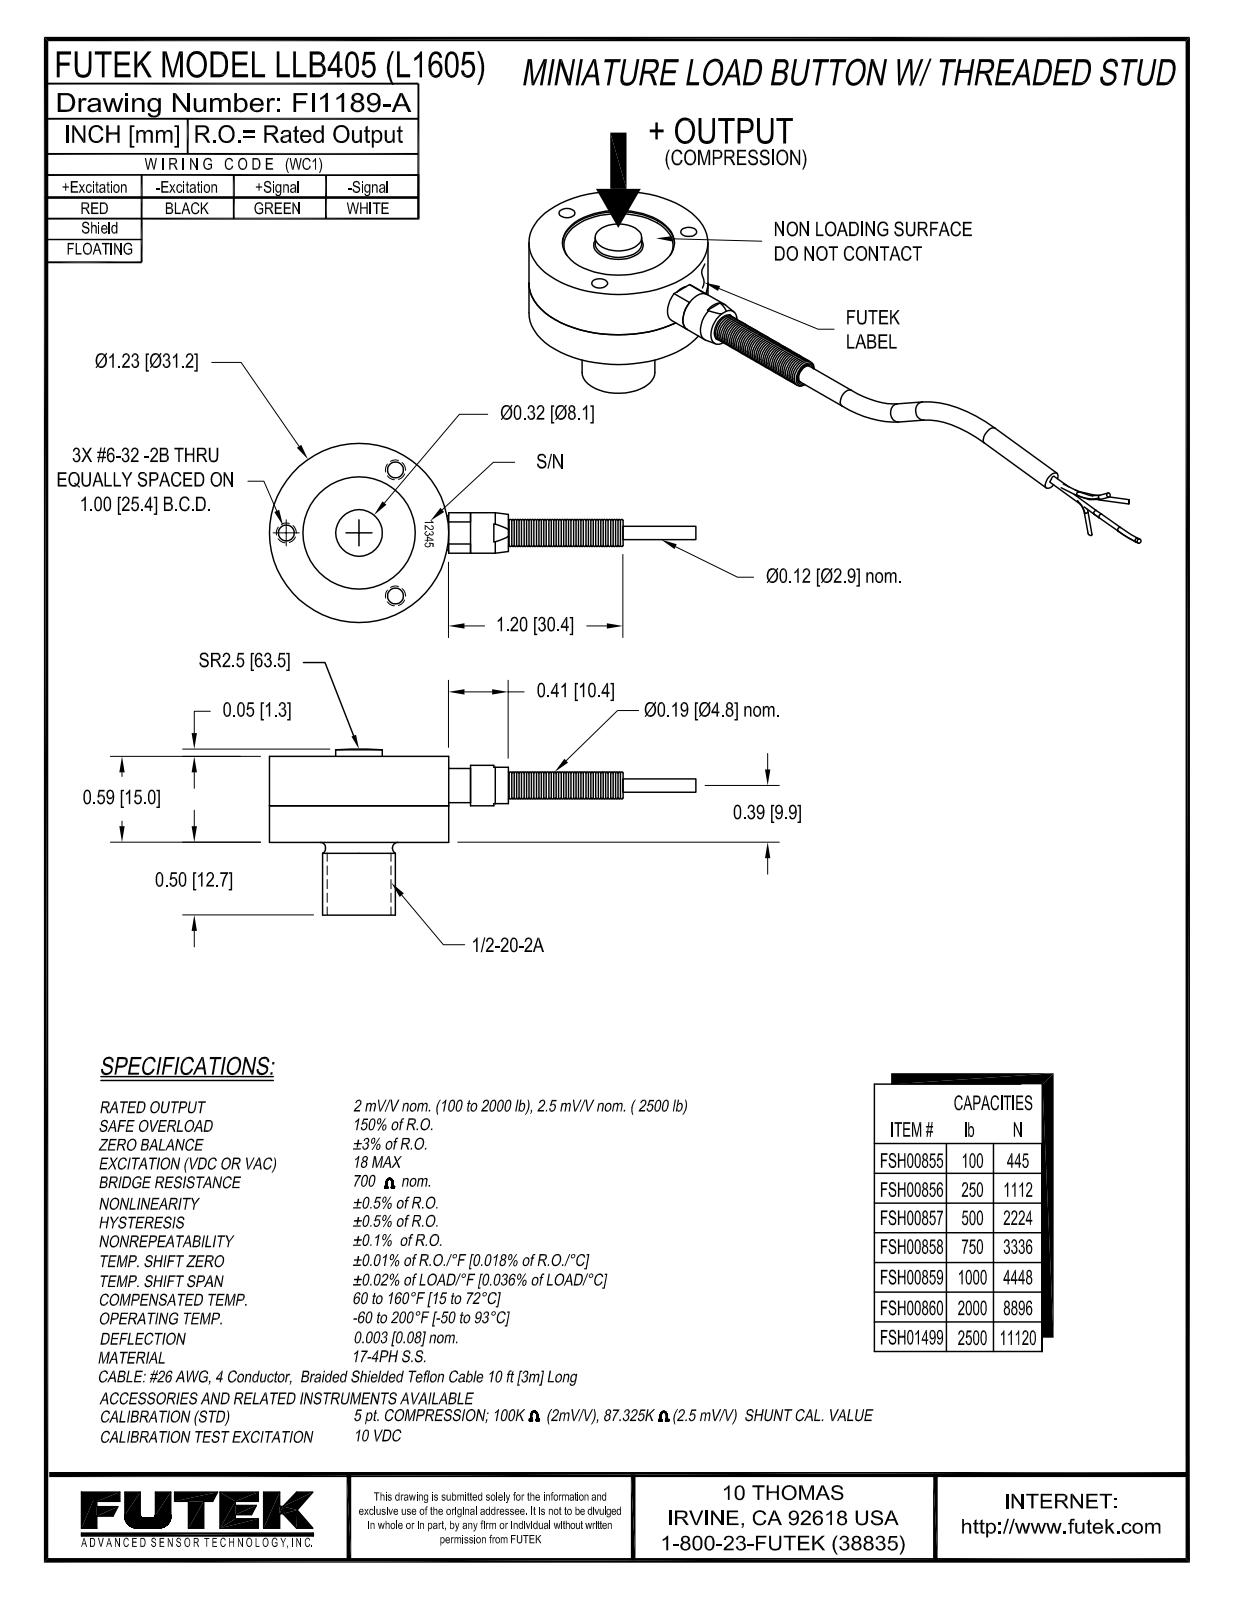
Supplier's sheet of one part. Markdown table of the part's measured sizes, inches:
| quantity | value |
| --- | --- |
| part name | LLB405 (LevelofDetail1); PART1 (~1); 2049; 2049A (+1 more) |
| STEP written by | Autodesk Inventor 2008 (AUTOMOTIVE_DESIGN) |
| units | inches |
| bodies | 3 solids, 213 faces (72 planar, 52 cylindrical, 89 other) |
| overall size | 5.084 × 1.389 × 1.23 |
| volume | 0.836 in³ |
| surface area | 9.284 in² |
| round holes (diameter × count) | 0.109 × 3, 0.13 × 1, 0.155 × 1, 0.161 × 1, 0.178 × 1, 0.189 × 1, 0.21 × 1, 0.228 × 1, 0.77 × 1 |
| round bosses / shafts (diameter × count) | 0.125 × 3, 1.23 × 1, 0.5 × 1, 0.46 × 1, 0.32 × 1, 0.278 × 1, 0.225 × 1, 0.205 × 1 |
| partial cylindrical surfaces (radius × count) | 0.083 × 1, 0.097 × 1 |
| main face-to-face distances | 0.59, 0.02, 0.57, 0.5, 1.07, 1.09, 0.25, 0.75, 0.32, 0.34 |
| hole center spacings | 0.5, 0.866 |
